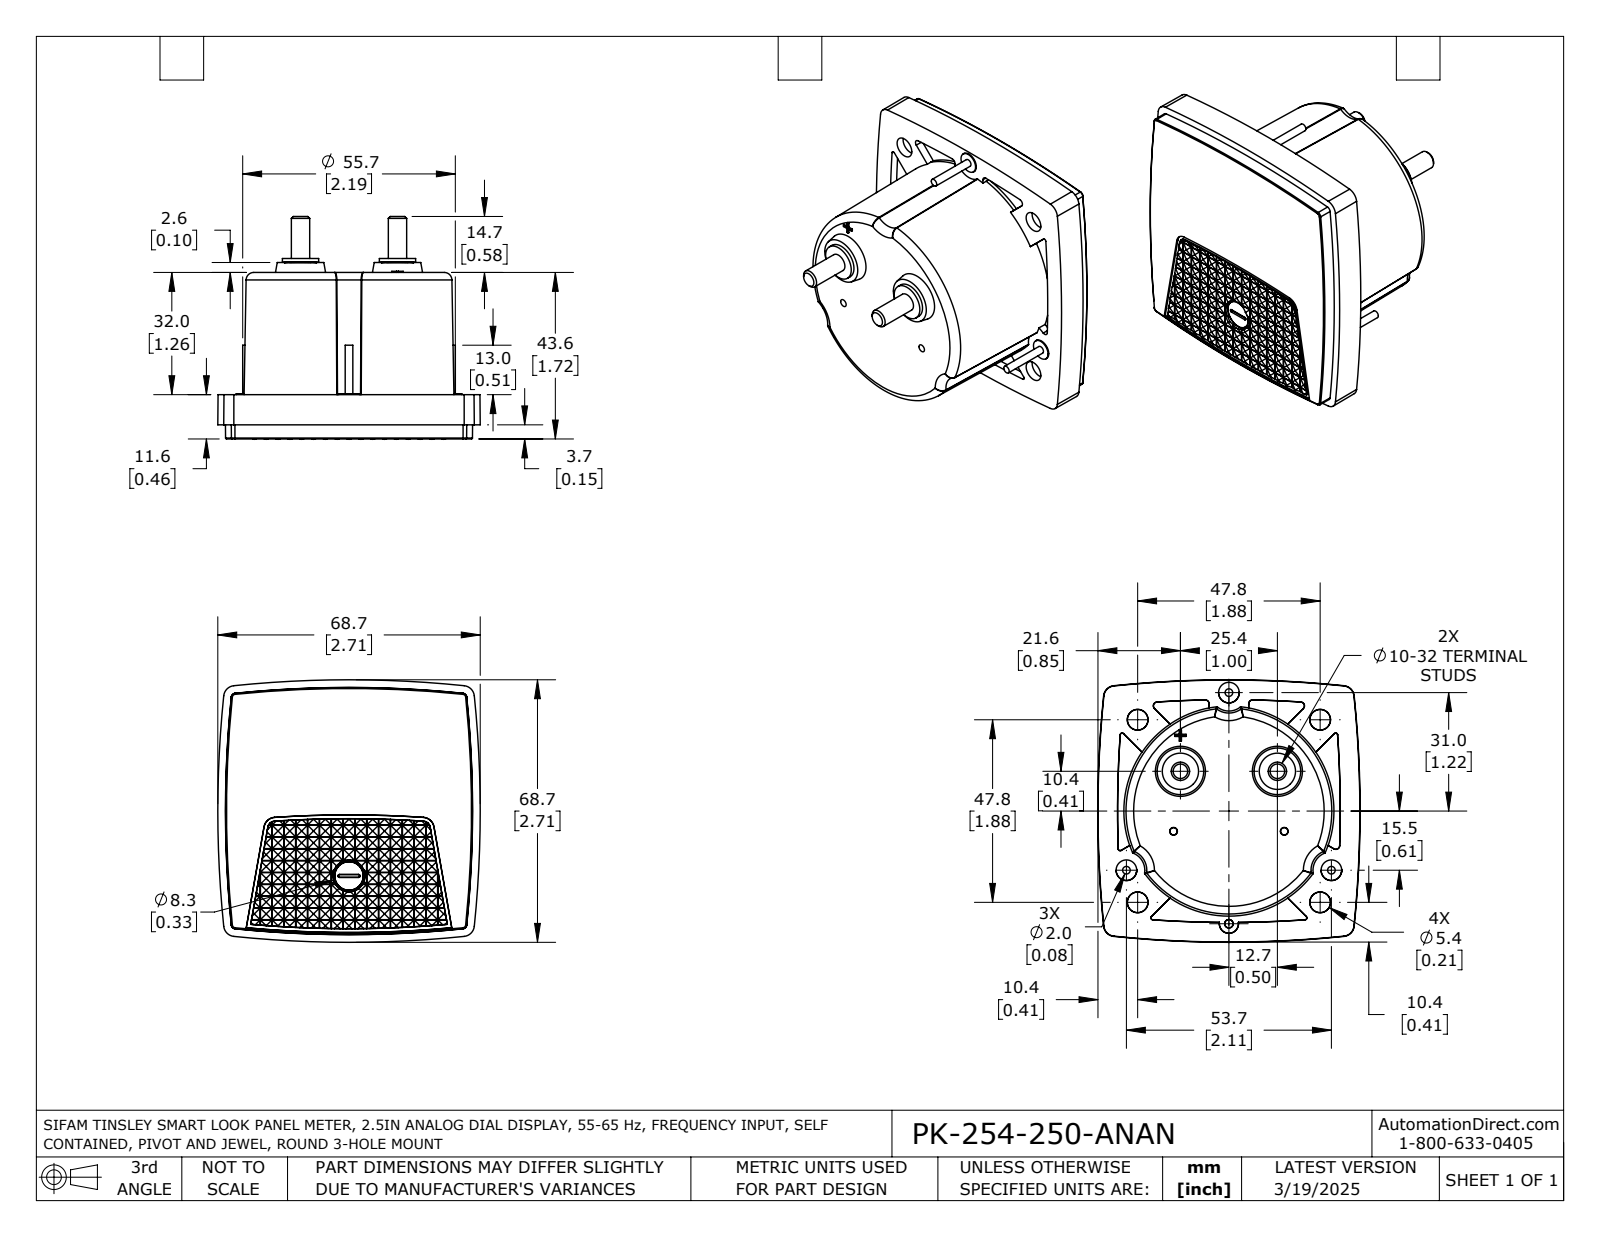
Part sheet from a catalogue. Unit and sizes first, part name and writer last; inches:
Units: inches
Overall size (bounding box): 2.706 × 2.706 × 2.297
Round bosses / shafts (diameter × count): ⌀0.213 ×3, ⌀0.079 ×3, ⌀0.374 ×2, ⌀0.189 ×2, ⌀0.215 ×1
Partial cylindrical surfaces — rounded edges, fillets, slot ends (radius × count): R0.167 ×2, R1.083 ×1
Main face-to-face distances: 1.717, 1.26, 0.457, 0.024, 0.087, 0.096, 0.311, 0.12, 0.072, 1.346
Volume: 7.594 in³ · Surface area: 30.41 in²
Bodies: 1 solid, 1550 faces (1165 planar, 265 cylindrical, 120 other)
Part name (STEP PRODUCT): PK-254-250-ANAN
STEP written by: SolidWorks 2021 (AUTOMOTIVE_DESIGN)
